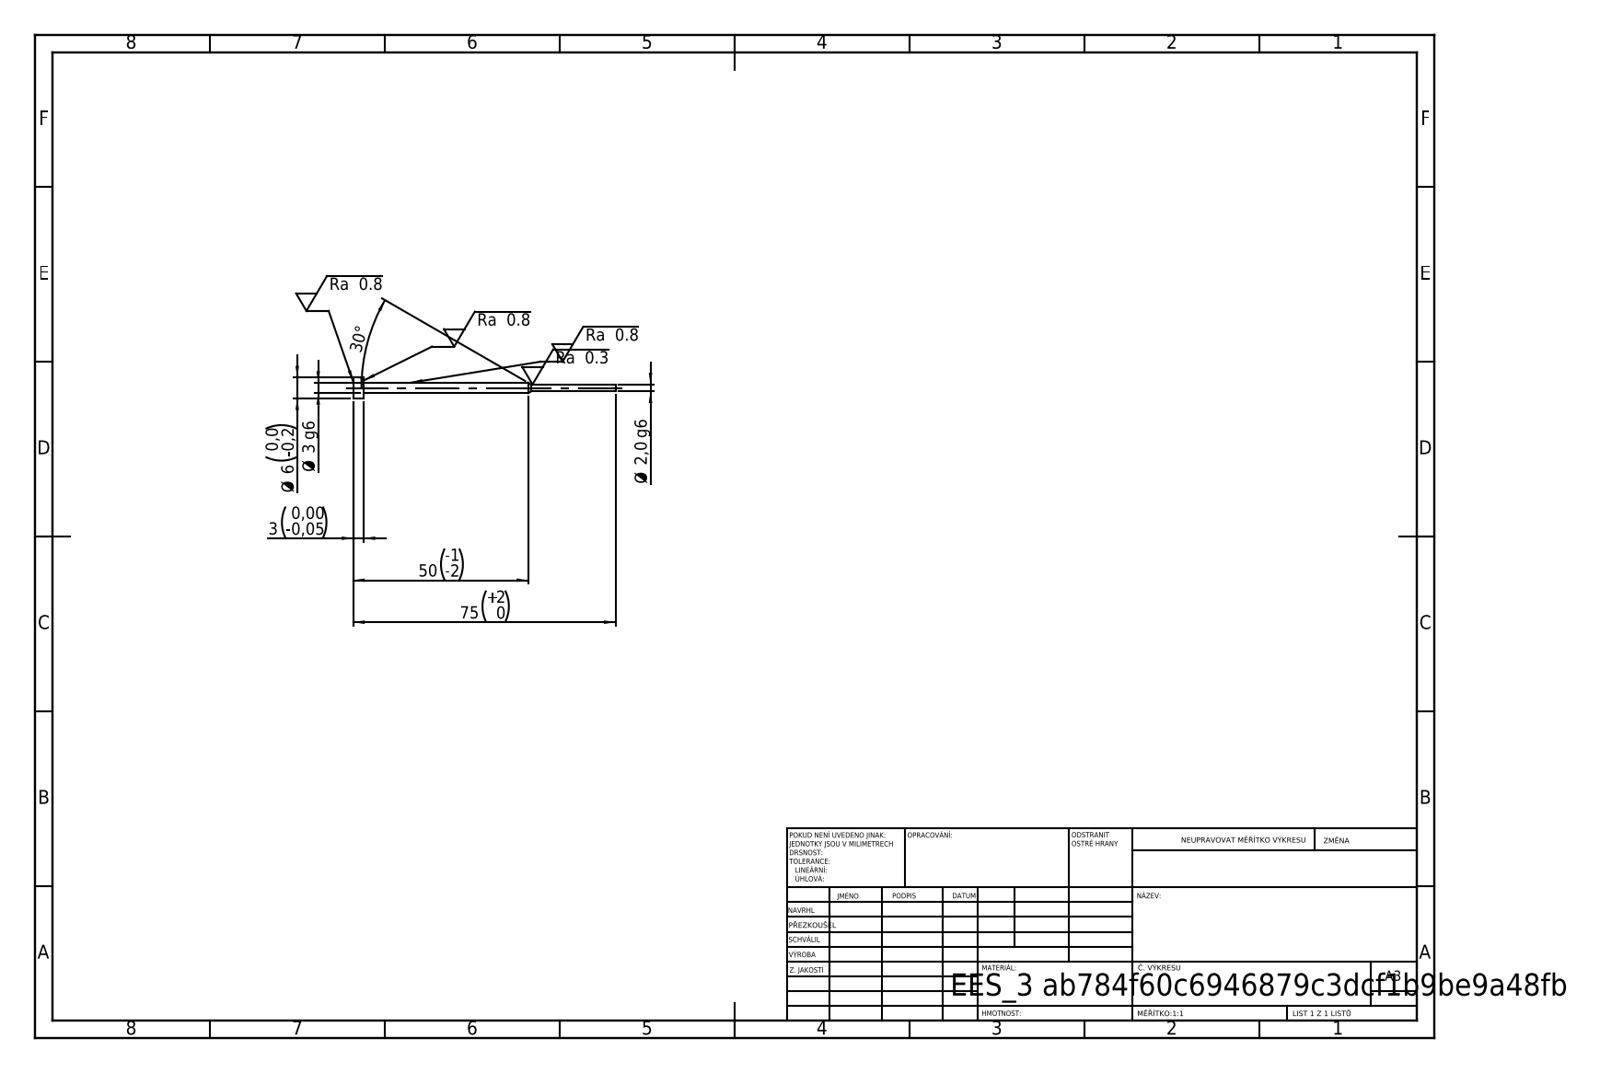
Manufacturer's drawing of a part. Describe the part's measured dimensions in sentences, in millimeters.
Its 3-D file was written by "SolidWorks 2019 (CONFIG_CONTROL_DESIGN)". It is 1 solid with 11 faces: 3 planar, 6 cylindrical and 2 other. Overall it measures 75 by 6 by 6 millimeters. Its volume is 497 cubic millimeters and its surface area 712 square millimeters. Round bosses or shafts: 1 of diameter 6, 1 of diameter 3, 1 of diameter 2. The main face-to-face distances are 3, 72, 75.
